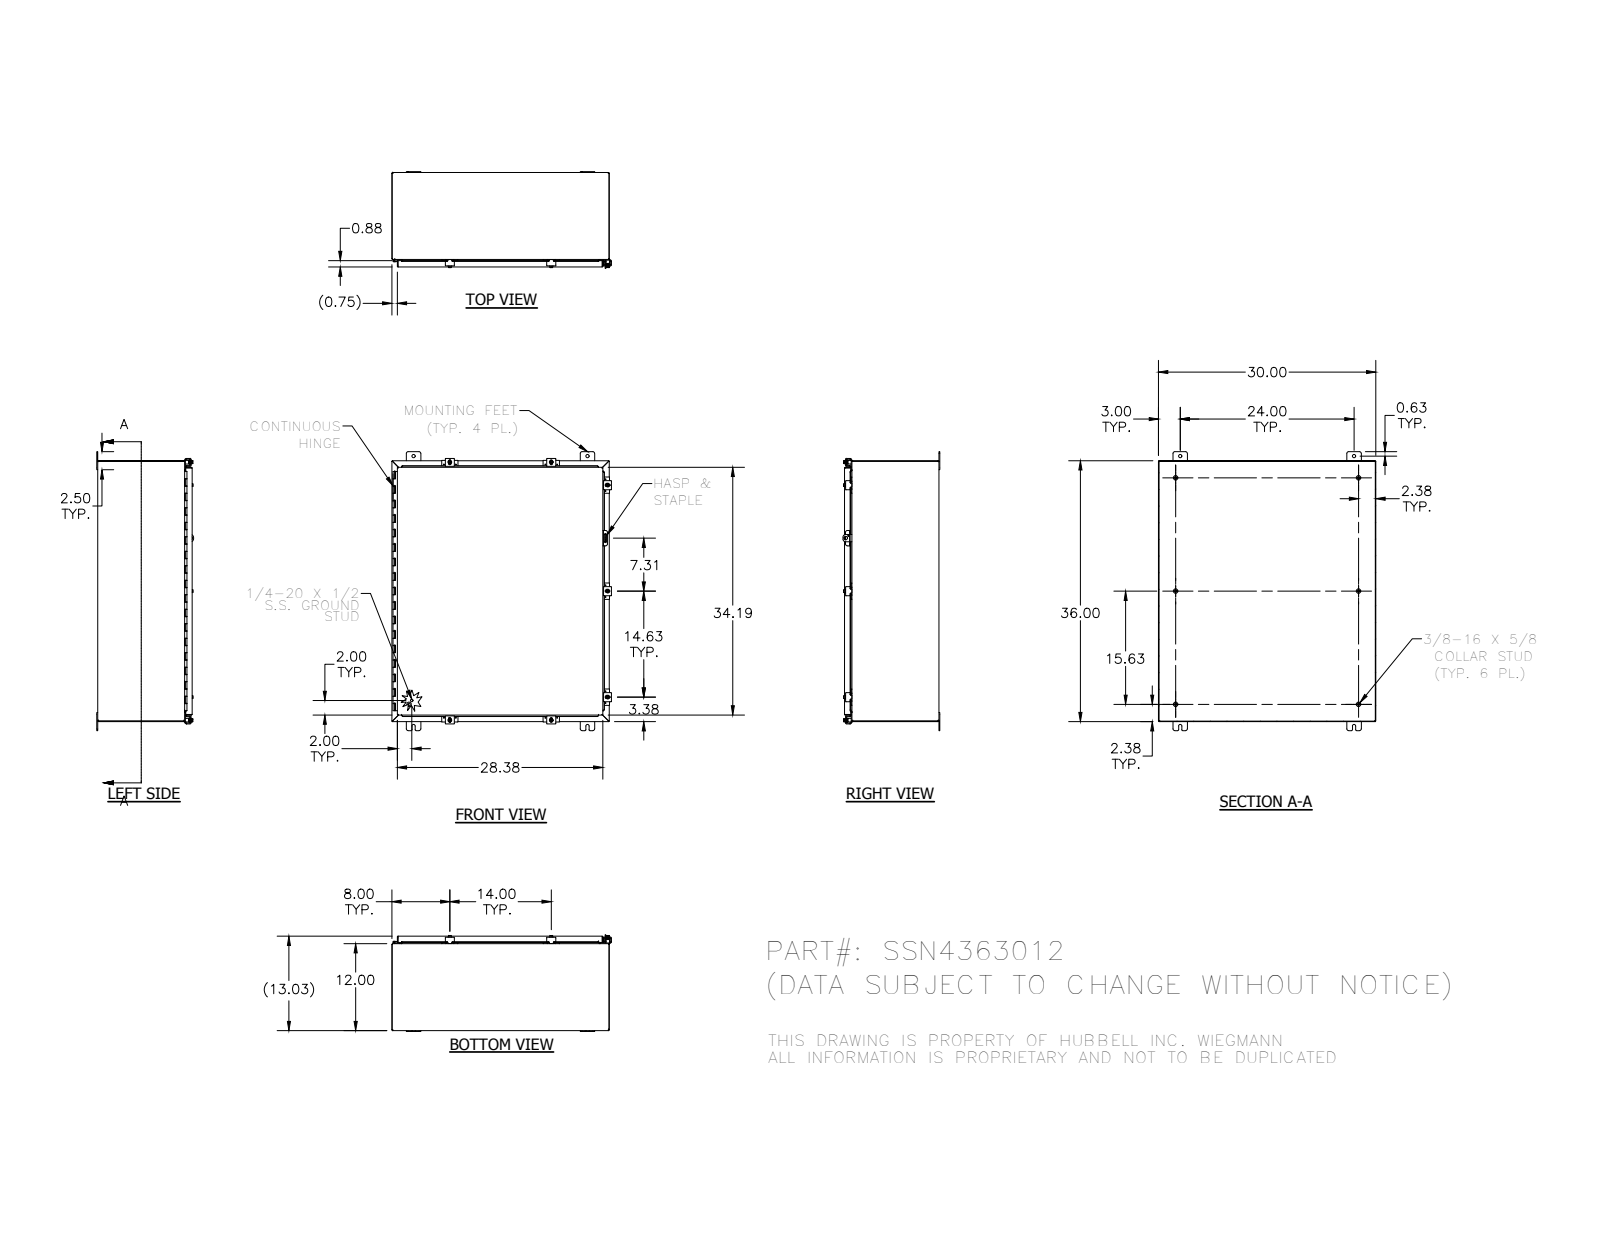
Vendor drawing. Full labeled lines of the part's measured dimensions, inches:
Part name (STEP PRODUCT): 30824-1; 30818; 38859; SSN4363012 (+8 more)
STEP written by: SolidWorks 2014 (AUTOMOTIVE_DESIGN)
Units: inches
Bodies: 54 solids, 2204 faces (846 planar, 983 cylindrical, 375 other)
Overall size (bounding box): 38.5 × 30.311 × 13.355
Volume: 322.2 in³ · Surface area: 8 523 in²
Round holes (diameter × count): ⌀0.11 ×14, ⌀0.211 ×7, ⌀0.281 ×7, ⌀0.3 ×7, ⌀0.438 ×4, ⌀0.125 ×1, ⌀0.156 ×1, ⌀0.5 ×1
Round bosses / shafts (diameter × count): ⌀0.25 ×9, ⌀0.52 ×7, ⌀0.5 ×7, ⌀0.35 ×7, ⌀0.625 ×6, ⌀0.33 ×6, ⌀0.115 ×2, ⌀0.337 ×1
Partial cylindrical surfaces — rounded edges, fillets, slot ends (radius × count): R0.03 ×83, R0.125 ×37, R0.25 ×33, R0.031 ×23, R0.105 ×23, R0.062 ×15, R0.141 ×14, R0.1 ×10
Main face-to-face distances: 0.074, 12.959, 12.885, 13.033, 29.926, 35.926, 30, 29.852, 36, 35.852
Hole centre spacings: 0.876, 35.298, 14, 1.625, 13.191, 14.816, 34.961, 34.998
